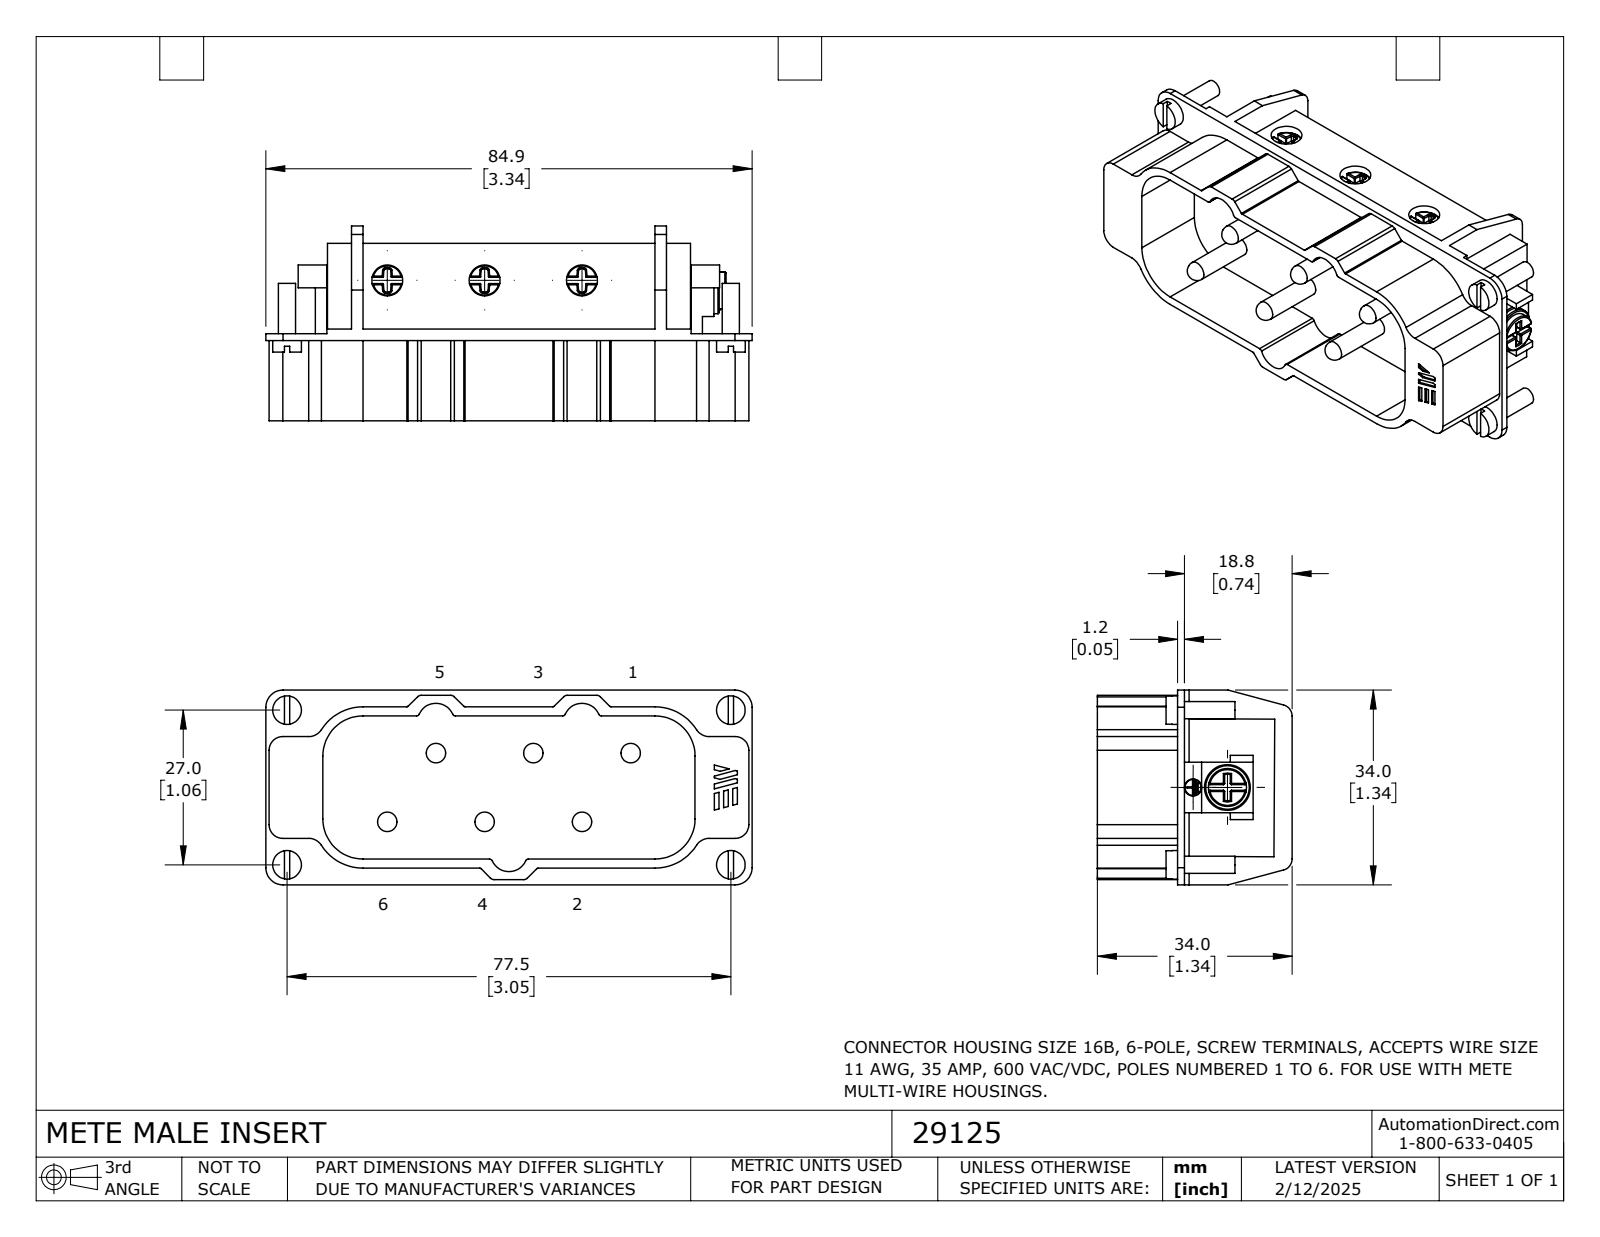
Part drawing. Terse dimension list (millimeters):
name: 29125
written by: SolidWorks 2024 (CONFIG_CONTROL_DESIGN)
unit: mm
bodies: 1 solid, 669 faces (303 planar, 238 cylindrical, 128 other)
size: 84.9 × 34 × 34
volume: 37 770 mm³; area: 19 150 mm²
holes: 6× ⌀4.6, 6× ⌀5.4, 1× ⌀3
bosses: 10× ⌀3, 6× ⌀3.4, 4× ⌀5, 1× ⌀8, 1× ⌀6.6, 1× ⌀2.8
rounds: 56× R0.2, 6× R0.3, 6× R0.5, 6× R0.9, 6× R3.4, 4× R2.4, 4× R2.6, 4× R3
face distances: 2, 1.6, 0.8, 26.6, 14, 24, 1.2, 1, 2.2, 13
hole spacings: 17, 8.5, 14.7, 34, 25.5, 28.2, 42.5, 44.2
